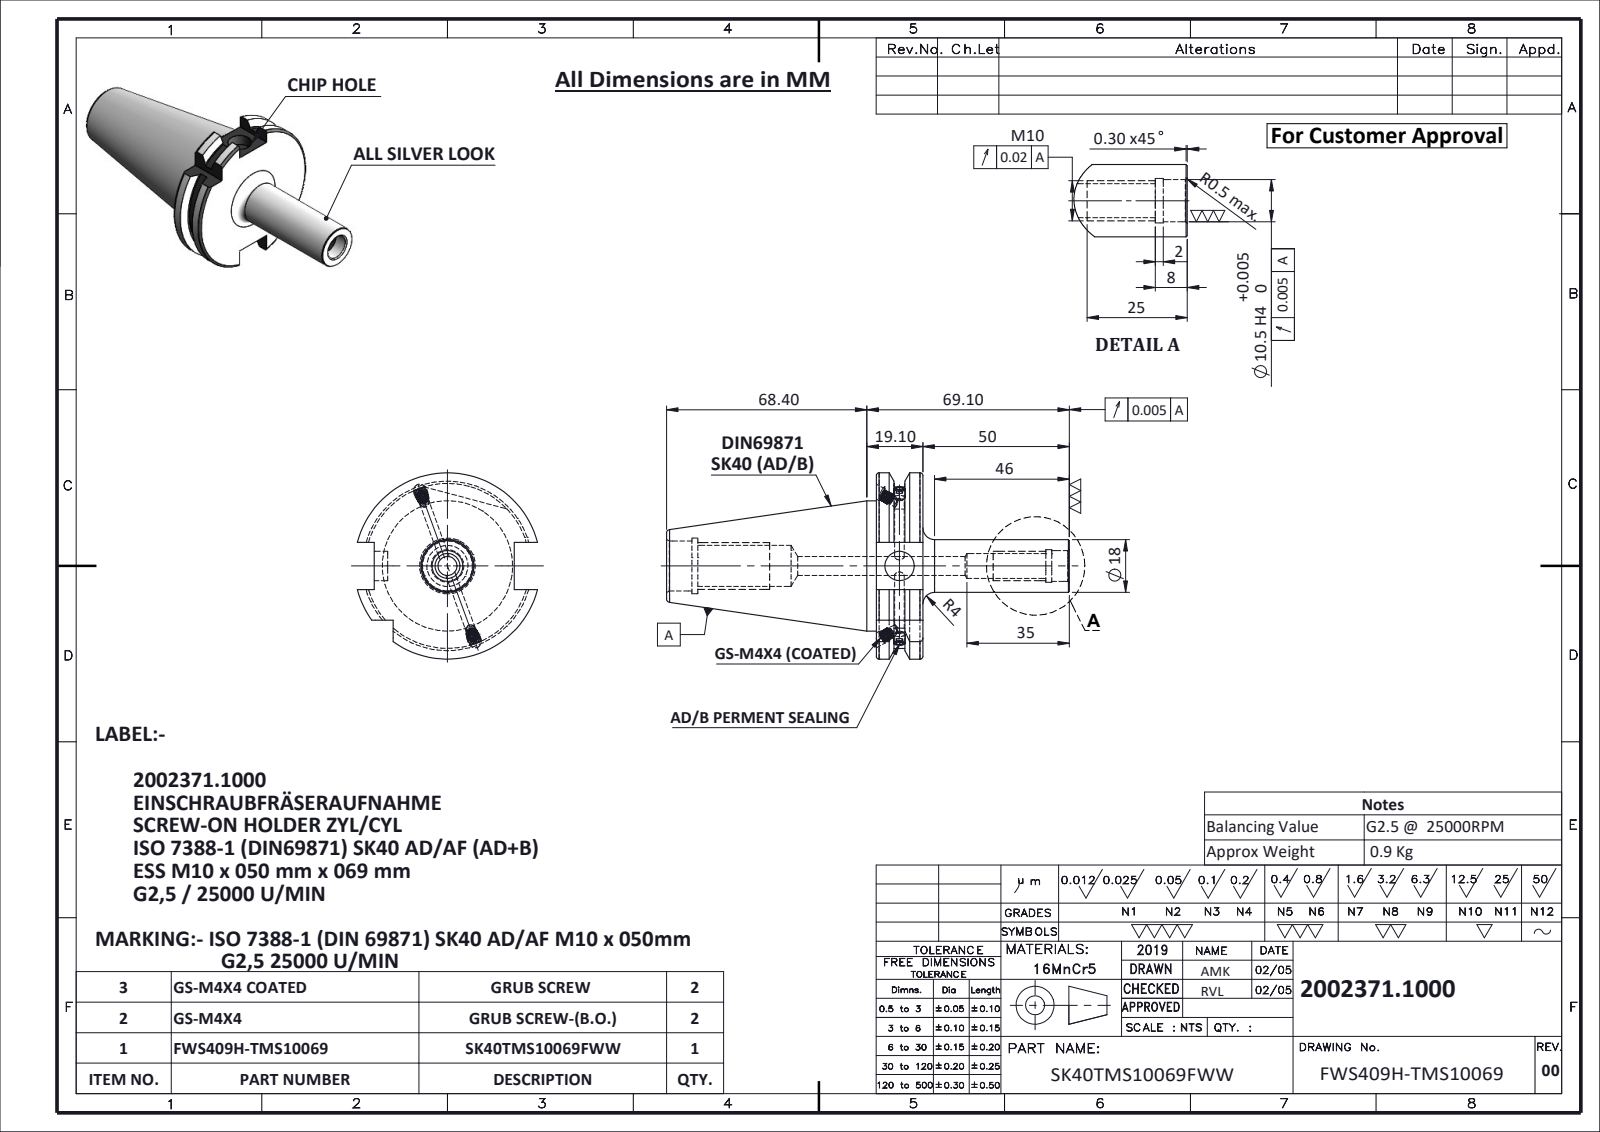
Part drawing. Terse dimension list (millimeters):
name: SK40TMS10069FWW; M4X4_DIN 913 - M4 x 4-N; GS-M4X4-COATING_DIN 913 - M4 x 4-N; FWS409H-TMS10069
written by: SolidWorks 2024 (CONFIG_CONTROL_DESIGN)
unit: mm
bodies: 5 solids, 242 faces (64 planar, 72 cylindrical, 106 other)
size: 137.5 × 63.55 × 61.48
volume: 113 886 mm³; area: 24 861 mm²
holes: 3× ⌀3.3, 2× ⌀4.5, 1× ⌀6.5, 1× ⌀8.5, 1× ⌀10, 1× ⌀10.5, 1× ⌀11.1, 1× ⌀14, 1× ⌀17, 1× ⌀19
bosses: 4× ⌀4, 2× ⌀2.9, 1× ⌀44.45, 1× ⌀18
rounds: 1× R28.12, 1× R31.77
face distances: 15.9, 16.1, 47.8, 71.6, 87.5, 137.5, 65.9, 50, 10.7, 60.9
